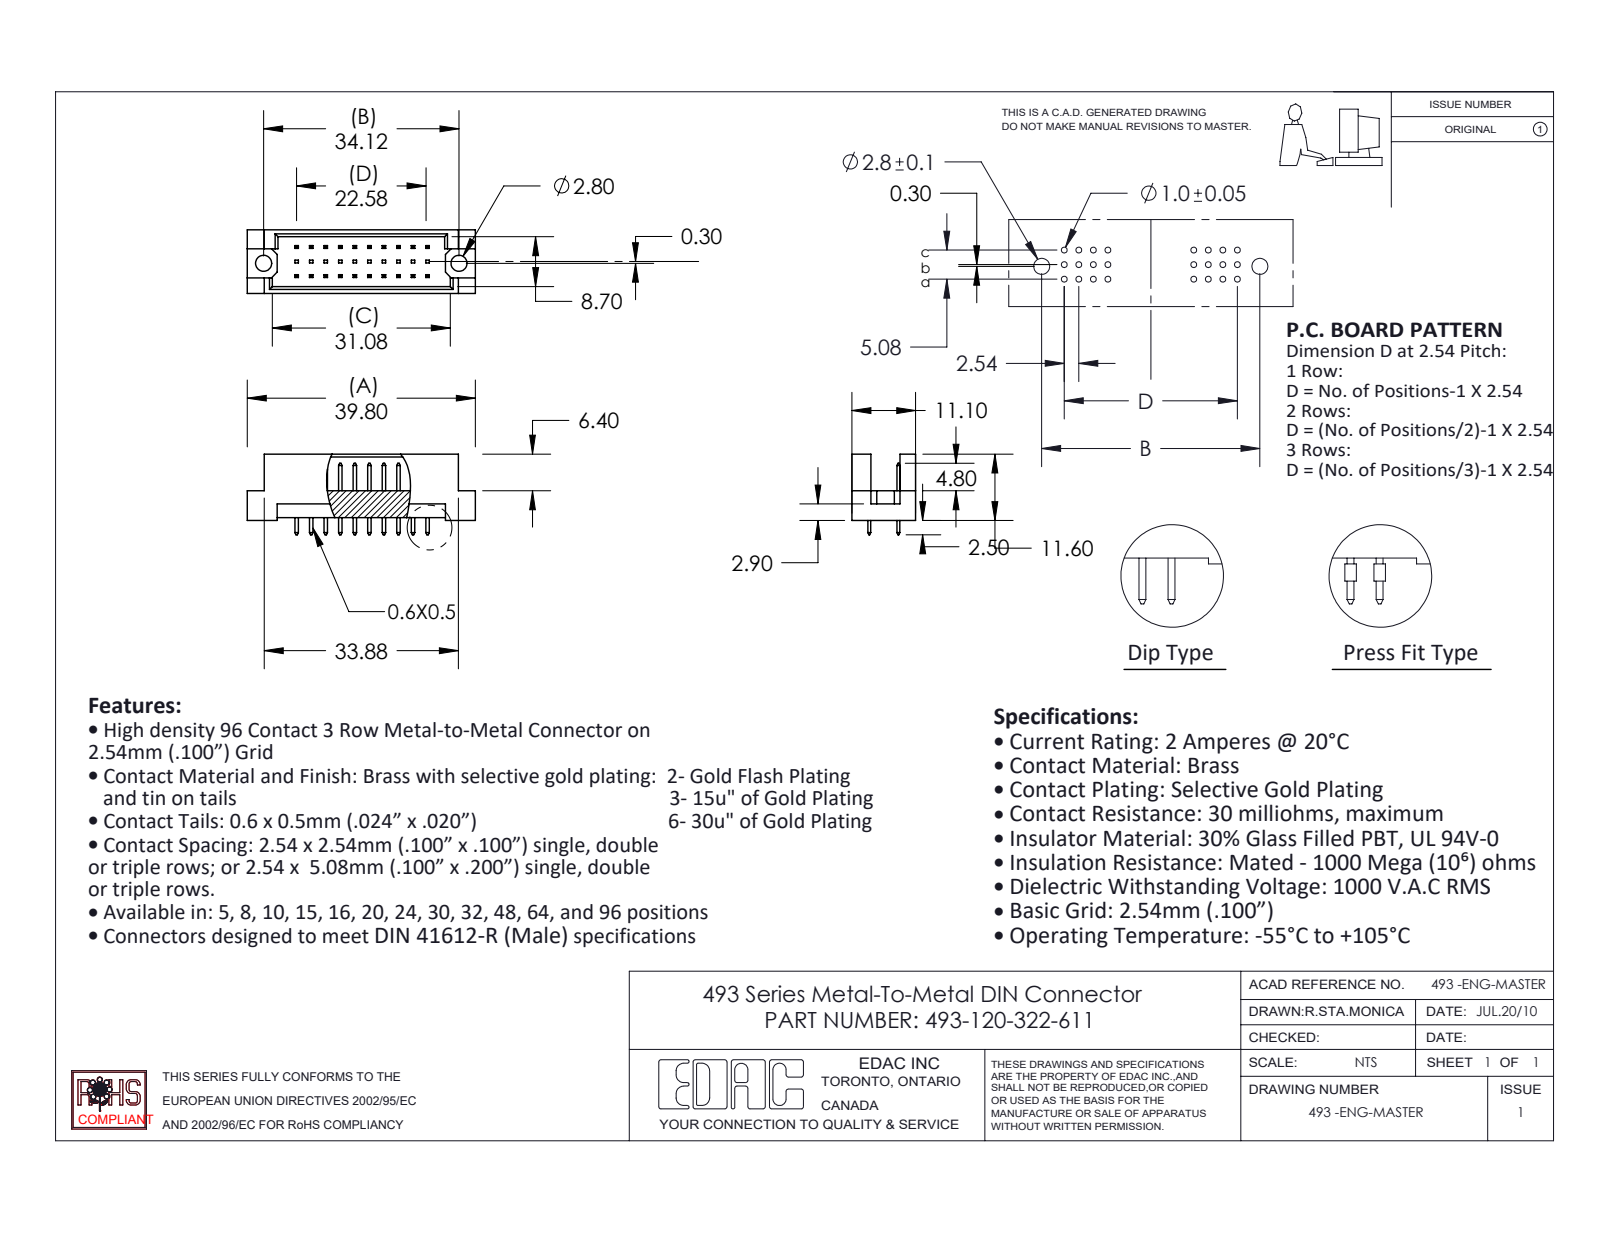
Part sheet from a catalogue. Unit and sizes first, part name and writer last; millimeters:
Units: millimetres
Overall size (bounding box): 39.8 × 14.1 × 11.1
Round holes (diameter × count): ⌀2.8 ×2
Main face-to-face distances: 1.2, 9.9, 5.08, 11.1, 2.54, 0.5, 8.7, 4.7, 2.76, 3.26
Hole centre spacings: 34.12
Volume: 2 446 mm³ · Surface area: 3 280 mm²
Bodies: 21 solids, 452 faces (448 planar, 4 cylindrical, 0 other)
Part name (STEP PRODUCT): 493 Part_30; 493-290_22; 493-124-322-321
STEP written by: SolidWorks 2020 (CONFIG_CONTROL_DESIGN)
